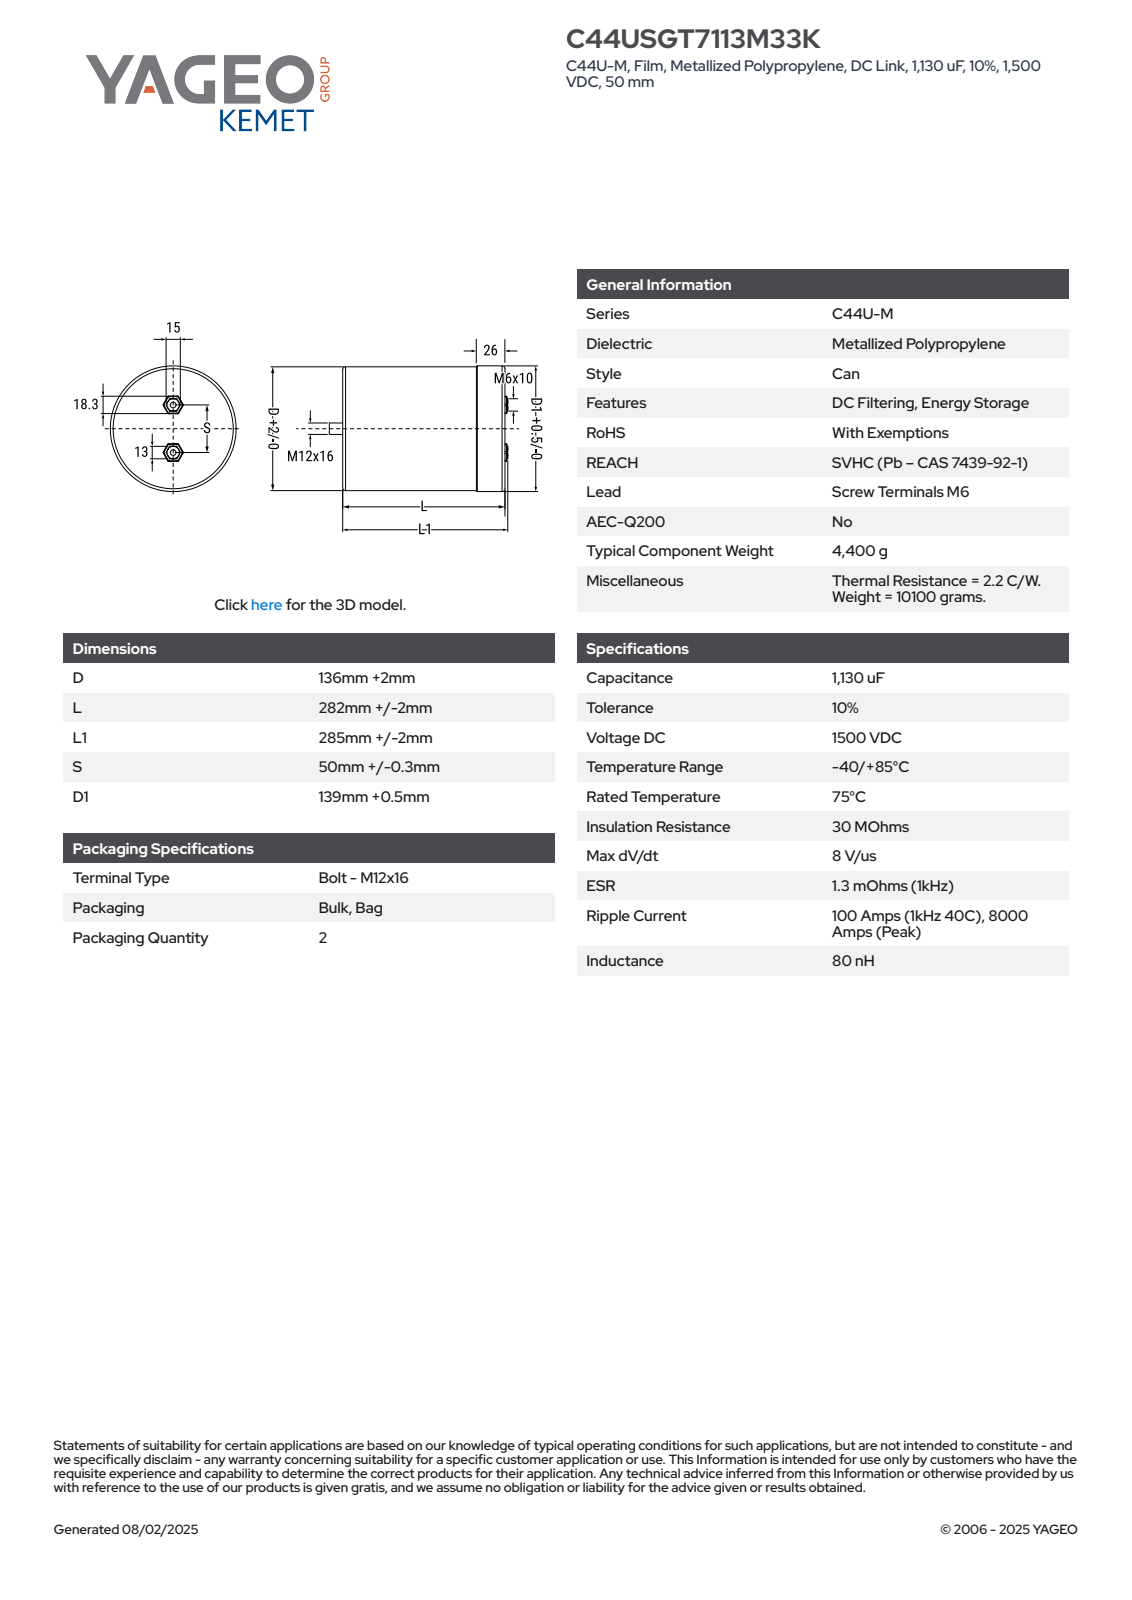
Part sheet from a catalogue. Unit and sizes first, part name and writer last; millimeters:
Units: millimetres
Overall size (bounding box): 303 × 139.5 × 139.5
Round holes (diameter × count): ⌀6 ×2
Round bosses / shafts (diameter × count): ⌀13 ×2, ⌀139.5 ×1, ⌀138 ×1, ⌀12 ×1
Partial cylindrical surfaces — rounded edges, fillets, slot ends (radius × count): R69.01 ×1
Main face-to-face distances: 284, 258, 26, 286, 28, 2, 287, 29, 3, 1
Hole centre spacings: 50
Volume: 4 259 000 mm³ · Surface area: 155 137 mm²
Bodies: 1 solid, 92 faces (44 planar, 17 cylindrical, 31 other)
Part name (STEP PRODUCT): CFP_C44UMH_136X282_D138L284S50L1287D1139.5
STEP written by: SolidWorks 2014 (AUTOMOTIVE_DESIGN)
